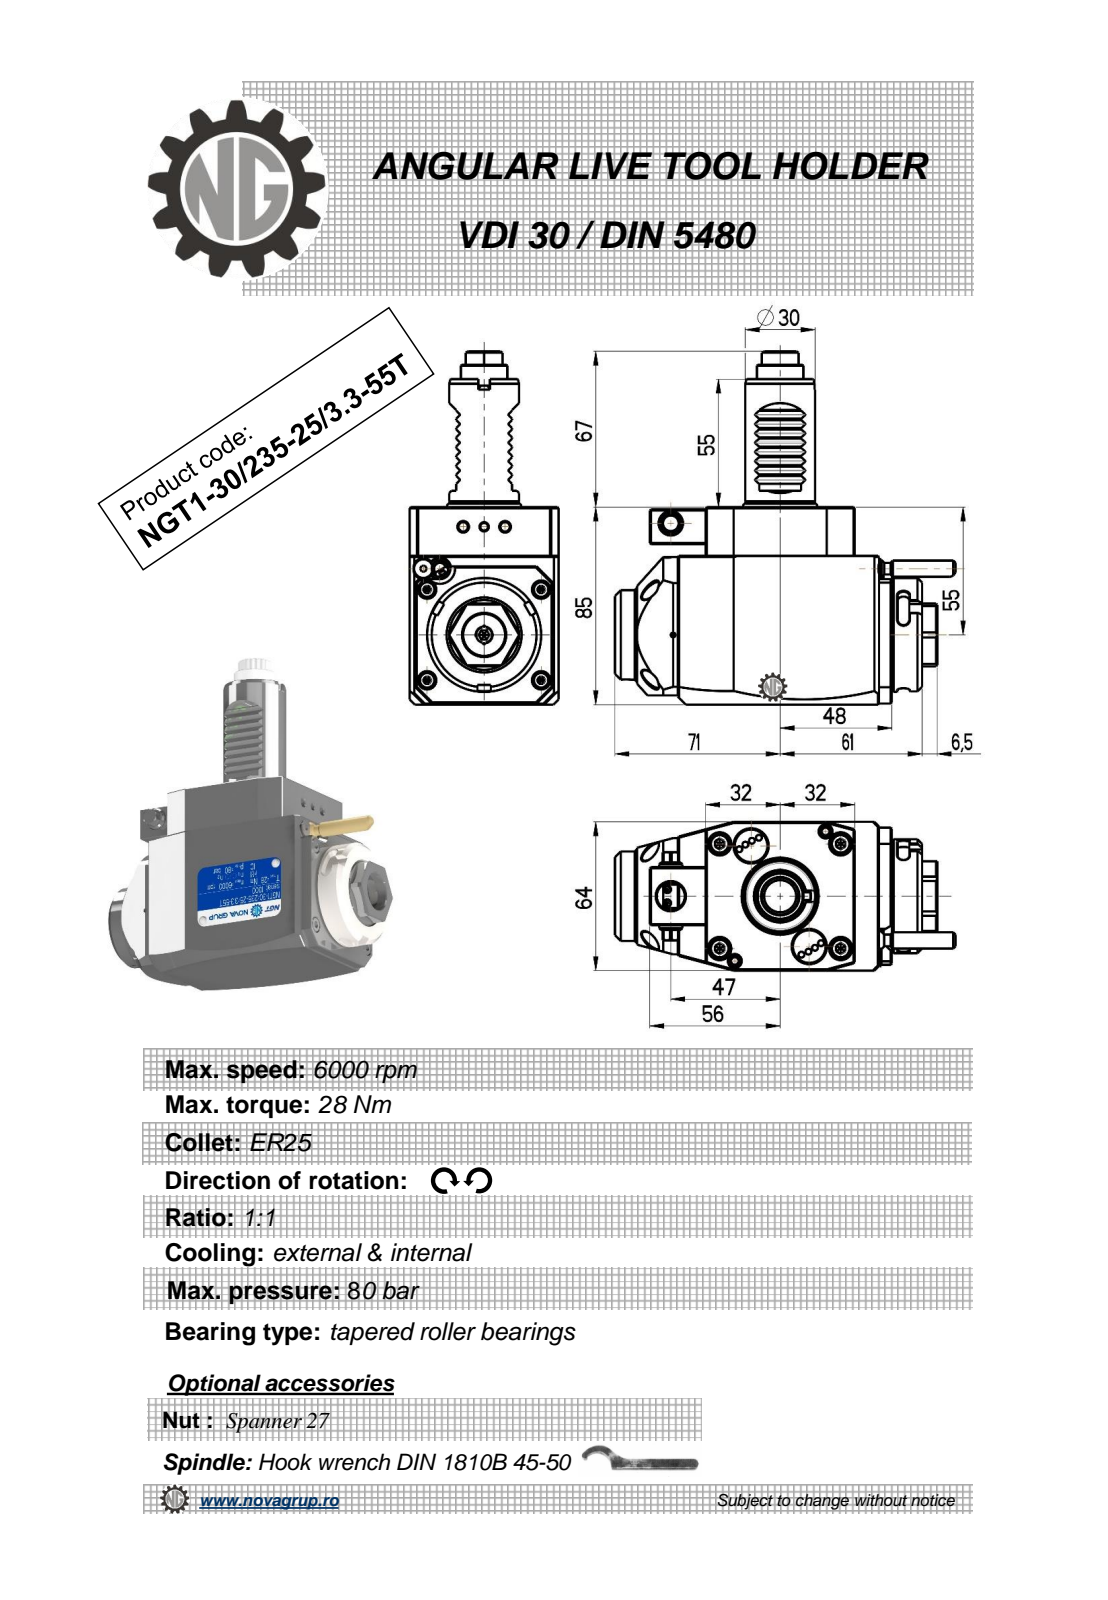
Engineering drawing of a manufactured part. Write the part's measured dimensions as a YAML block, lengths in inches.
part_name: "NGT1_30_235_25_3_3_55T"
step_written_by: "PRO/ENGINEER BY PARAMETRIC TECHNOLOGY CORPORATION, 2010280 (CONFIG_CONTROL_DESIGN)"
units: inches
bodies: {solids: 1, faces: 472, planar: 217, cylindrical: 163, other: 92}
overall_size: [5.984, 5.763, 2.52]
volume: 34.66
surface_area: 80.76
round_holes:
  - {diameter: 0.098, count: 1}
  - {diameter: 0.118, count: 1}
  - {diameter: 0.374, count: 1}
  - {diameter: 0.472, count: 1}
  - {diameter: 0.709, count: 1}
round_bosses_or_shafts:
  - {diameter: 0.315, count: 2}
  - {diameter: 1.929, count: 1}
  - {diameter: 1.654, count: 1}
  - {diameter: 1.516, count: 1}
  - {diameter: 1.181, count: 1}
  - {diameter: 0.787, count: 1}
  - {diameter: 0.394, count: 1}
  - {diameter: 0.276, count: 1}
partial_cylinders:
  - {radius: 0.078, count: 36}
  - {radius: 0.012, count: 16}
  - {radius: 0.098, count: 6}
  - {radius: 7.087, count: 2}
  - {radius: 0.152, count: 1}
  - {radius: 0.167, count: 1}
  - {radius: 0.177, count: 1}
  - {radius: 0.279, count: 1}
face_to_face_distances: [2.52, 3.346, 0.63, 0.512, 0.827, 3.15, 1.142, 0.787, 0.02, 0.111]
hole_center_spacings: [1.03, 1.348, 1.831]
